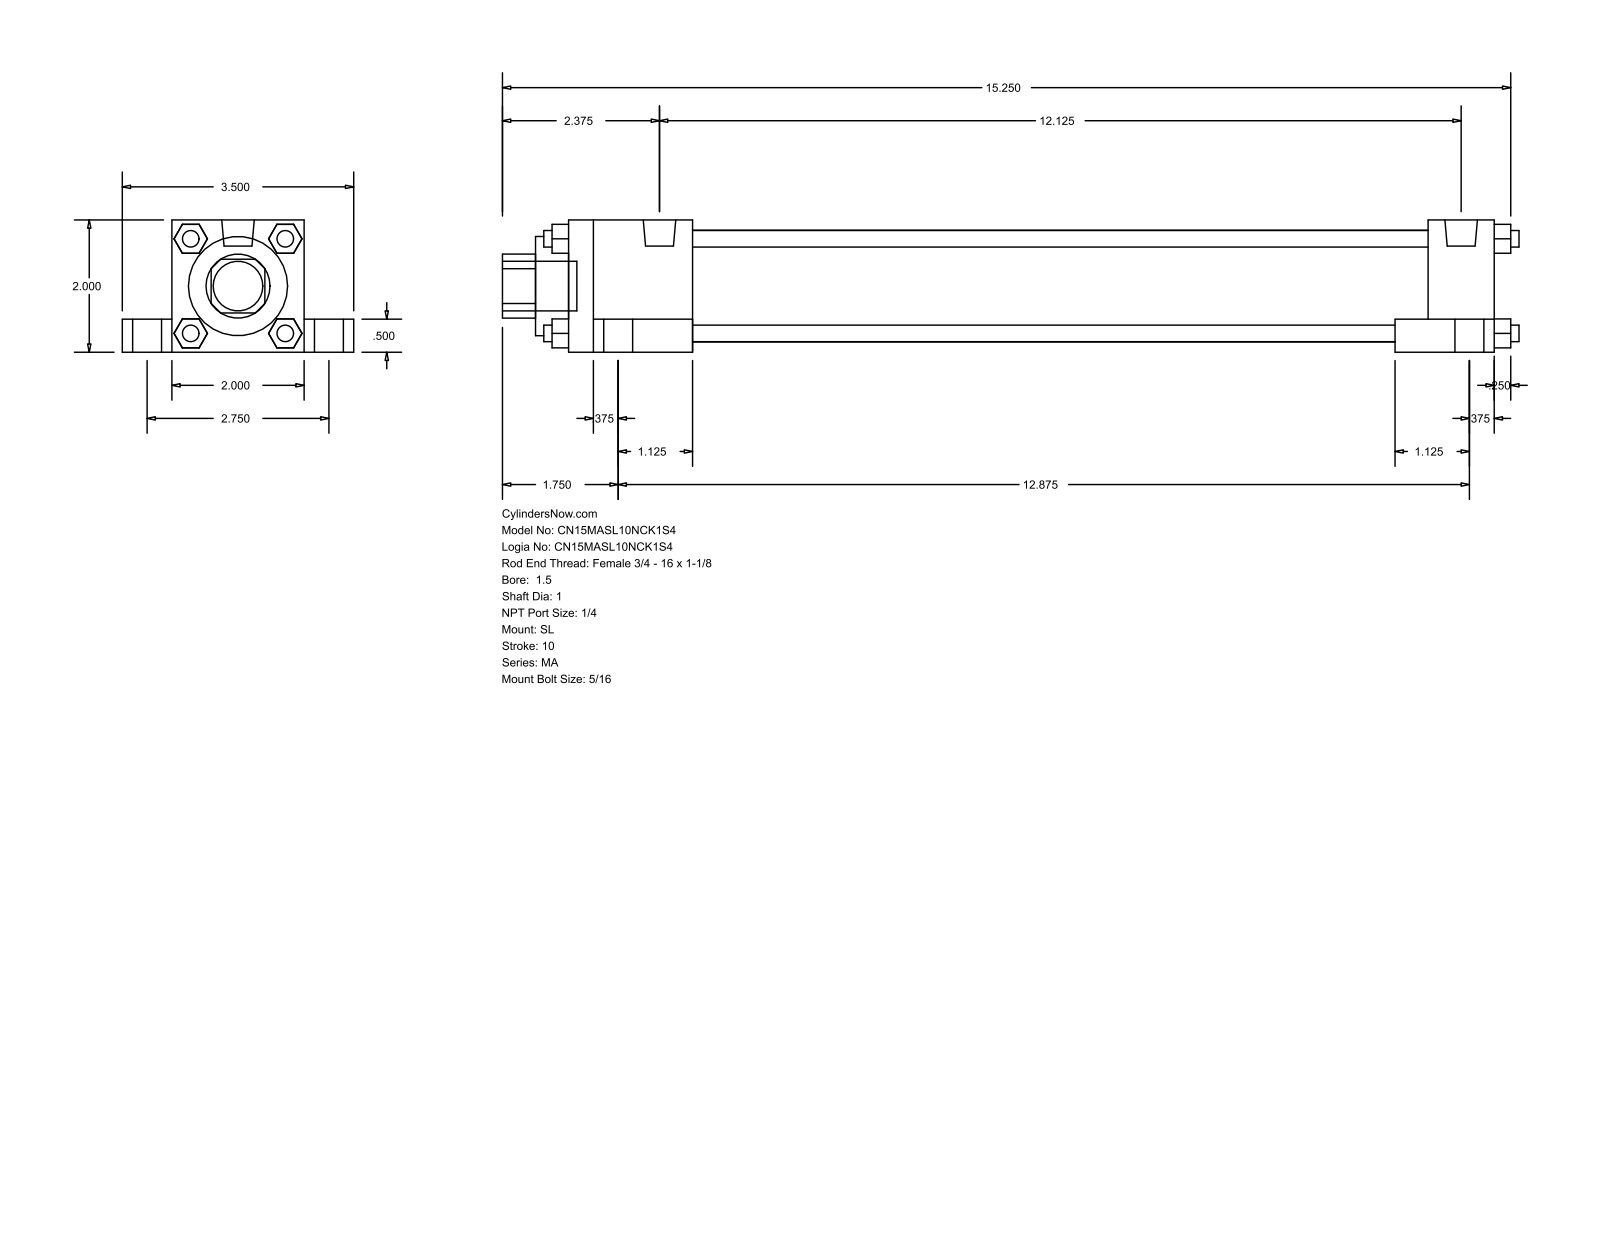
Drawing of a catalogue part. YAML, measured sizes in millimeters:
part_name: "MA_SL__0150_1"
step_written_by: "GSSL Pune (CONFIG_CONTROL_DESIGN)"
units: millimeters
bodies: {solids: 0, faces: 148, planar: 112, cylindrical: 36, other: 0}
overall_size: [390.52, 88.9, 50.8]
round_holes:
  - {diameter: 25.4, count: 1}
  - {diameter: 38.1, count: 1}
  - {diameter: 42.93, count: 1}
round_bosses_or_shafts:
  - {diameter: 17.46, count: 4}
  - {diameter: 11.11, count: 4}
  - {diameter: 7.94, count: 4}
  - {diameter: 6.35, count: 4}
  - {diameter: 12.49, count: 2}
  - {diameter: 19.05, count: 1}
partial_cylinders:
  - {radius: 12.29, count: 1}
face_to_face_distances: [50.8, 12.7, 19.05, 9.52, 69.85, 38.1, 6.35, 355.6, 25.4, 330.2]
